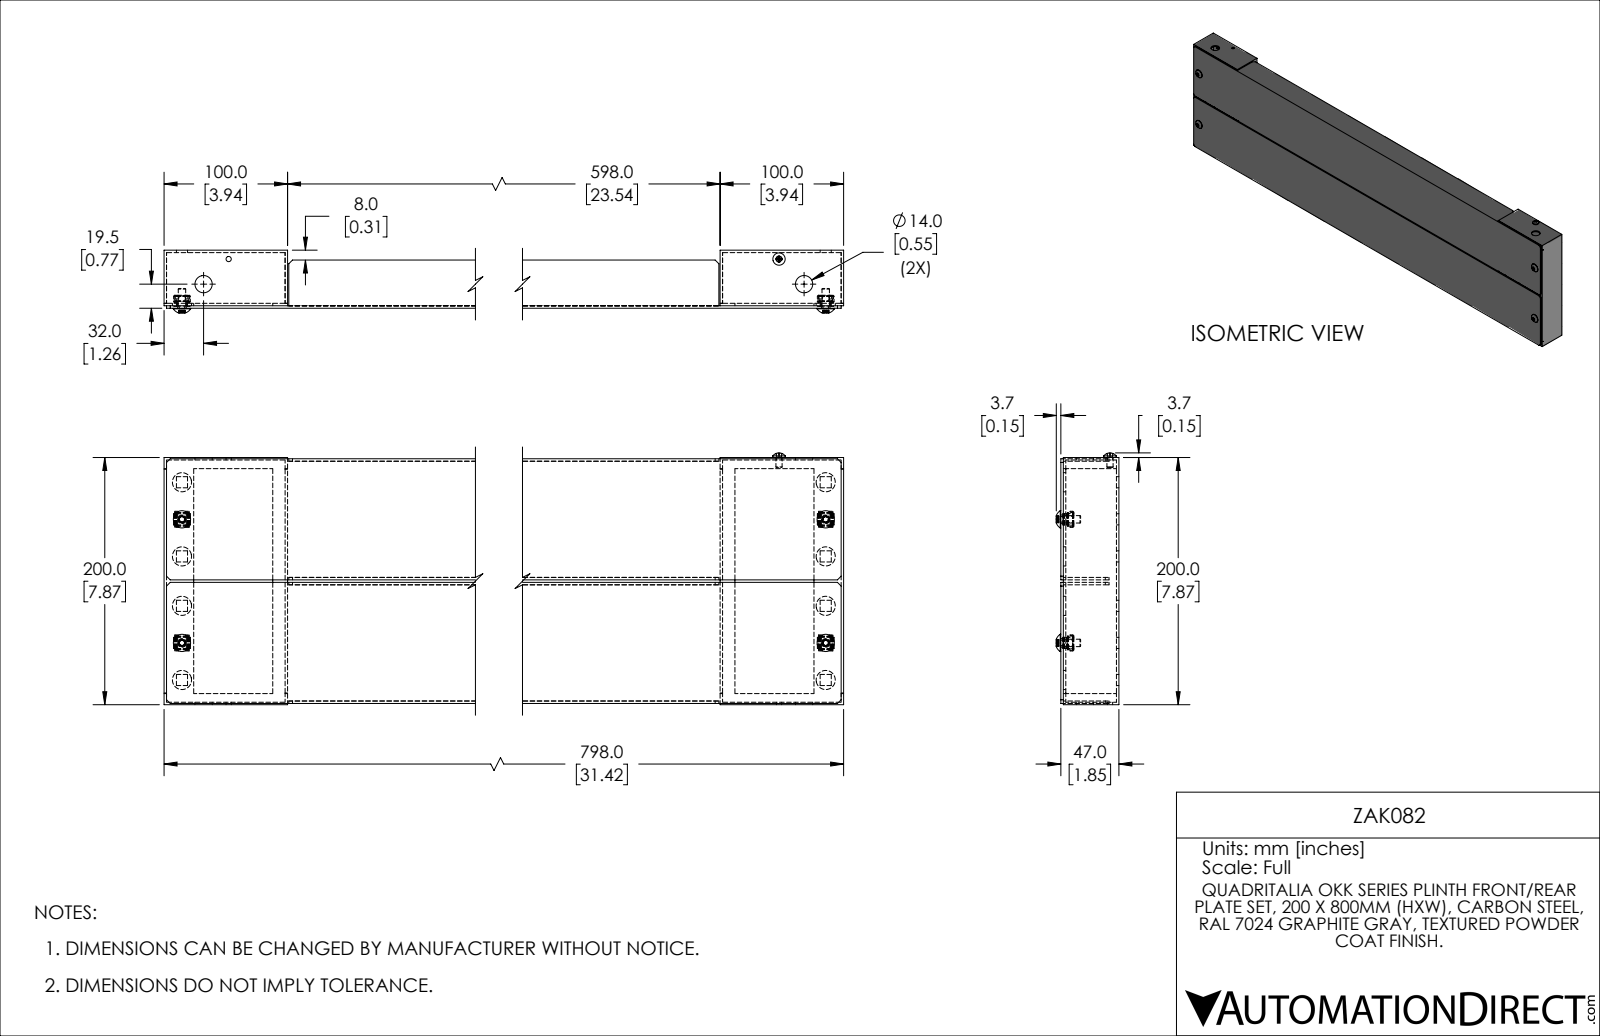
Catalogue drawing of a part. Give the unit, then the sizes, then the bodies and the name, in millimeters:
Units: millimetres
Overall size (bounding box): 798 × 203.7 × 50.7
Round holes (diameter × count): ⌀15.5 ×8, ⌀7 ×4, ⌀4.2 ×2, ⌀4.9 ×2, ⌀4.9 ×2, ⌀14 ×2
Round bosses / shafts (diameter × count): ⌀14 ×4, ⌀6 ×4, ⌀10 ×1, ⌀5 ×1
Partial cylindrical surfaces — rounded edges, fillets, slot ends (radius × count): R0.5 ×68, R0.3 ×48, R1 ×20
Main face-to-face distances: 2, 98, 100, 96, 45, 4, 196, 43, 1, 94
Hole centre spacings: 30, 769.6, 100, 769, 775.5, 60, 70, 130
Volume: 696 800 mm³ · Surface area: 711 000 mm²
Bodies: 17 solids, 738 faces (470 planar, 250 cylindrical, 18 other)
Part name (STEP PRODUCT): ZAK082
STEP written by: SolidWorks 2021 (CONFIG_CONTROL_DESIGN)
